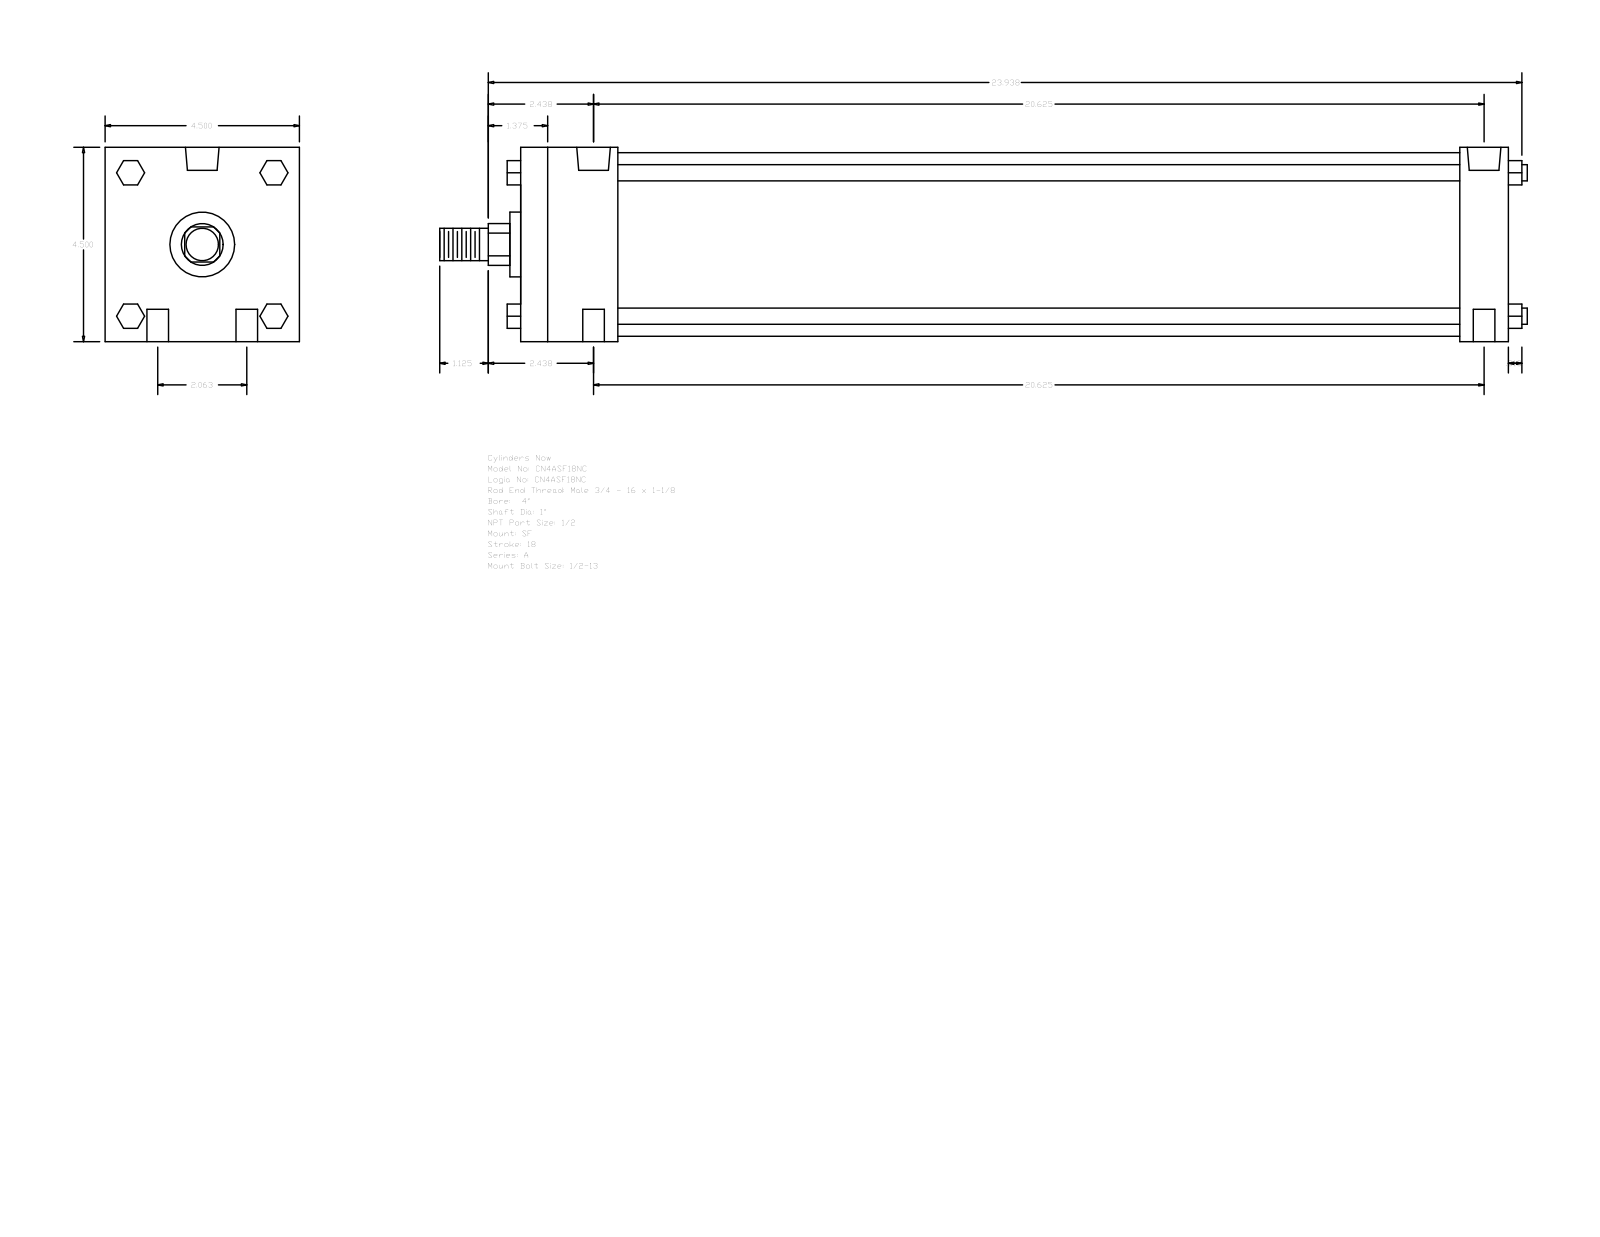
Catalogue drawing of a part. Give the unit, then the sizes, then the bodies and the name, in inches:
Units: inches
Overall size (bounding box): 25.187 × 4.5 × 4.5
Round holes (diameter × count): ⌀0.5 ×4, ⌀0.344 ×2, ⌀0.778 ×2
Round bosses / shafts (diameter × count): ⌀0.375 ×4, ⌀4.25 ×1, ⌀1.5 ×1, ⌀1 ×1, ⌀0.75 ×1
Partial cylindrical surfaces — rounded edges, fillets, slot ends (radius × count): R0.484 ×1
Main face-to-face distances: 4.5, 22.875, 21.75, 1.125, 2.25, 19.5, 20.625, 0.563, 1.66, 2.875
Hole centre spacings: 1.031, 20.651, 20.625, 2.062, 20.728, 20.375
Bodies: 0 solids, 124 faces (94 planar, 30 cylindrical, 0 other)
Part name (STEP PRODUCT): A_SF__0400_1
STEP written by: GSSL Pune (CONFIG_CONTROL_DESIGN)
